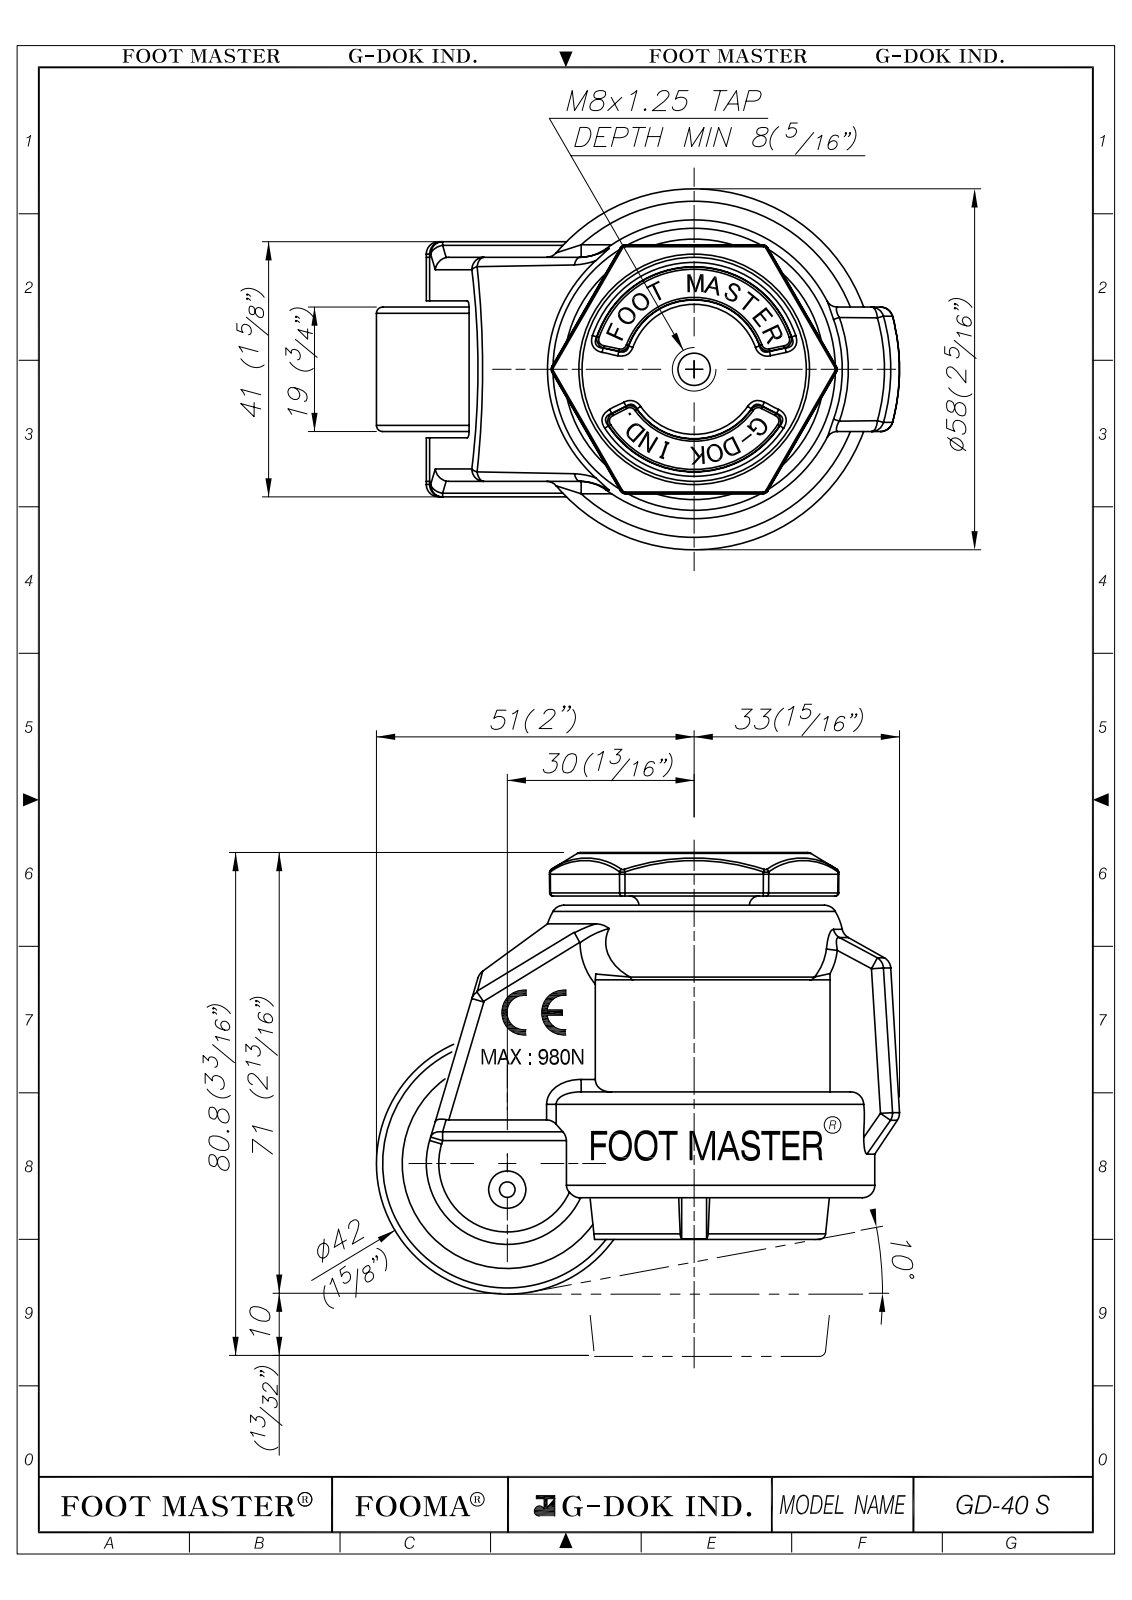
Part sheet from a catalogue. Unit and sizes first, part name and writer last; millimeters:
Units: millimetres
Overall size (bounding box): 83.96 × 70.8 × 58
Round holes (diameter × count): ⌀6 ×2, ⌀5 ×1, ⌀5.4 ×1, ⌀7 ×1, ⌀7.1 ×1, ⌀18 ×1, ⌀22 ×1, ⌀32 ×1, ⌀48 ×1
Round bosses / shafts (diameter × count): ⌀2.6 ×3, ⌀42 ×1, ⌀30 ×1, ⌀23.5 ×1, ⌀17.8 ×1, ⌀15 ×1, ⌀8 ×1, ⌀7 ×1
Partial cylindrical surfaces — rounded edges, fillets, slot ends (radius × count): R0.5 ×85, R1 ×58, R2 ×4, R1.25 ×1, R2.62 ×1, R3.6 ×1, R5 ×1, R13 ×1
Main face-to-face distances: 7, 1, 8, 21, 28, 29, 24, 14, 17, 30.5
Hole centre spacings: 1.1, 4.46, 5.56
Volume: 119 598 mm³ · Surface area: 47 997 mm²
Bodies: 6 solids, 1261 faces (362 planar, 277 cylindrical, 622 other)
Part name (STEP PRODUCT): GD-40S
STEP written by: Autodesk Inventor 2009 (AUTOMOTIVE_DESIGN)
